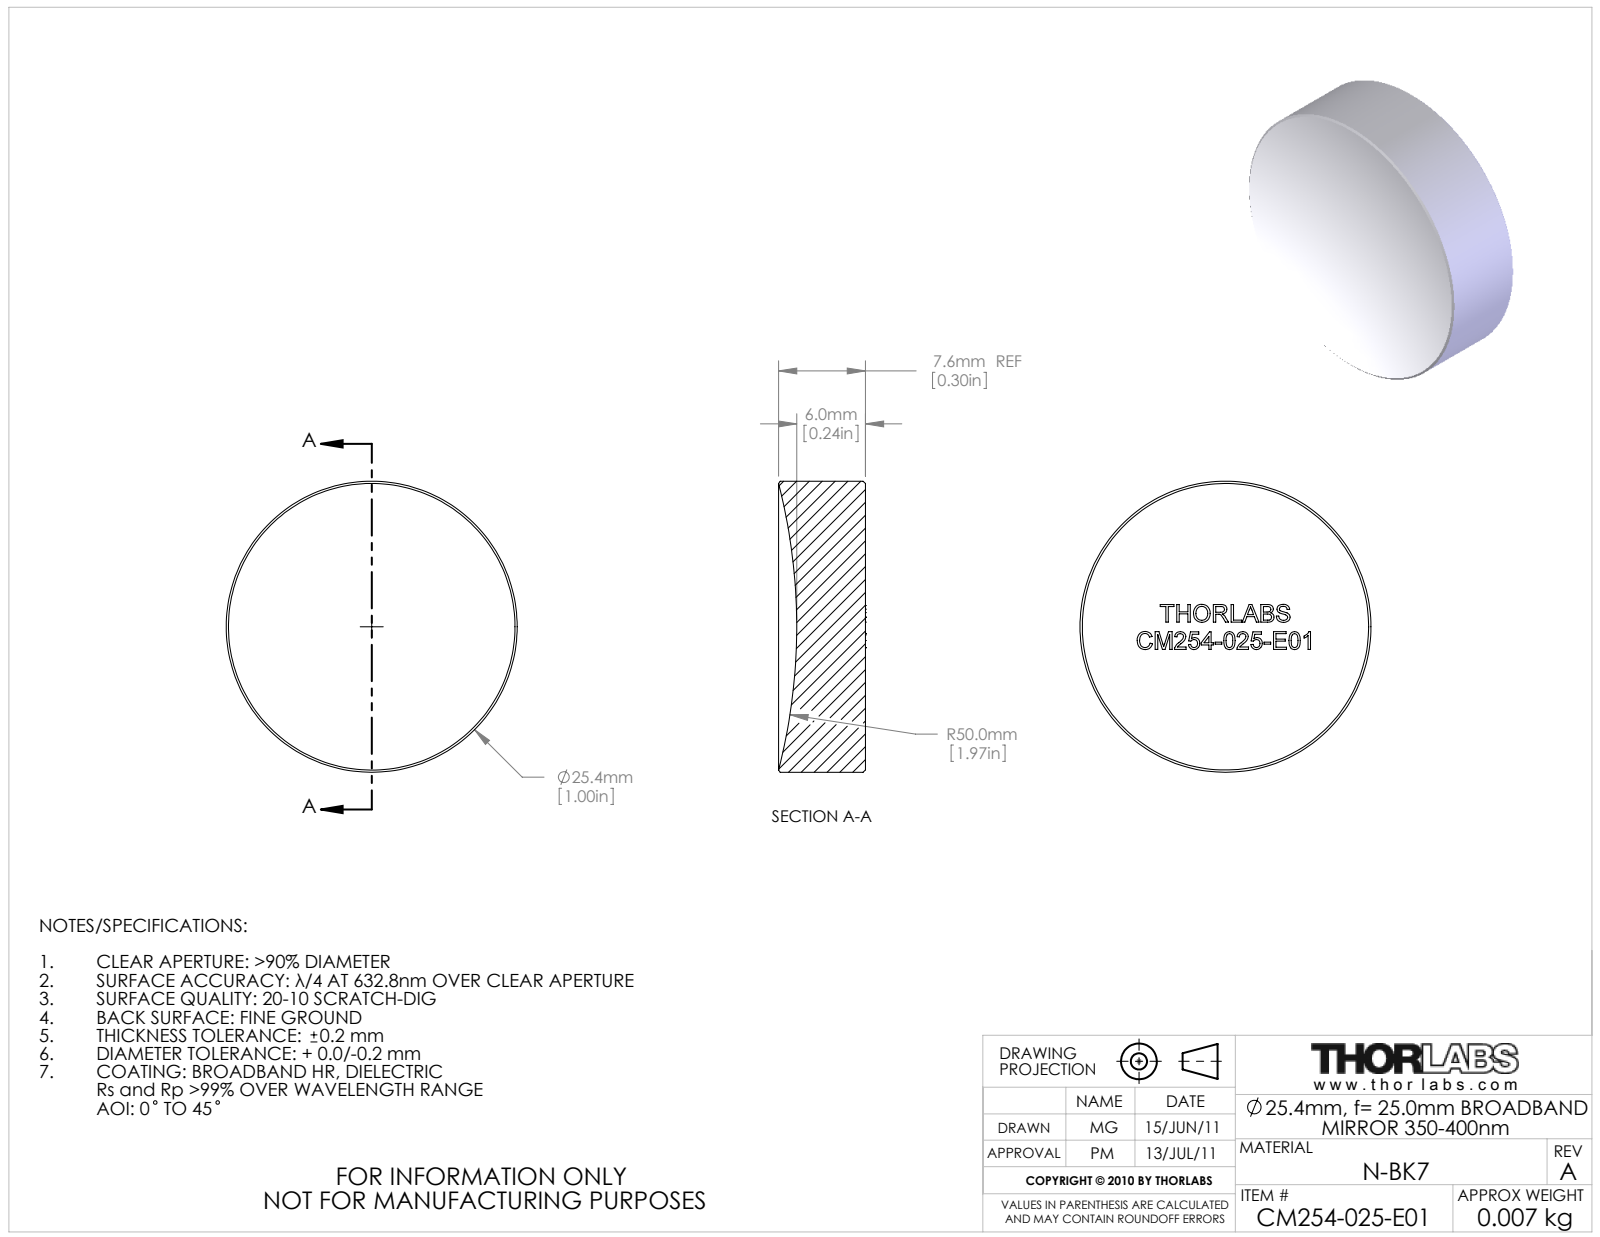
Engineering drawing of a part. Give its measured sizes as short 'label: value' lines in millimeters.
name: 22611-E0W
written by: SolidWorks 2011 (AUTOMOTIVE_DESIGN)
unit: mm
bodies: 0 solids, 44 faces (33 planar, 2 cylindrical, 9 other)
size: 25.4 × 25.4 × 7.59
bosses: 1× ⌀25.4
face distances: 3.91, 3.02, 0.89
